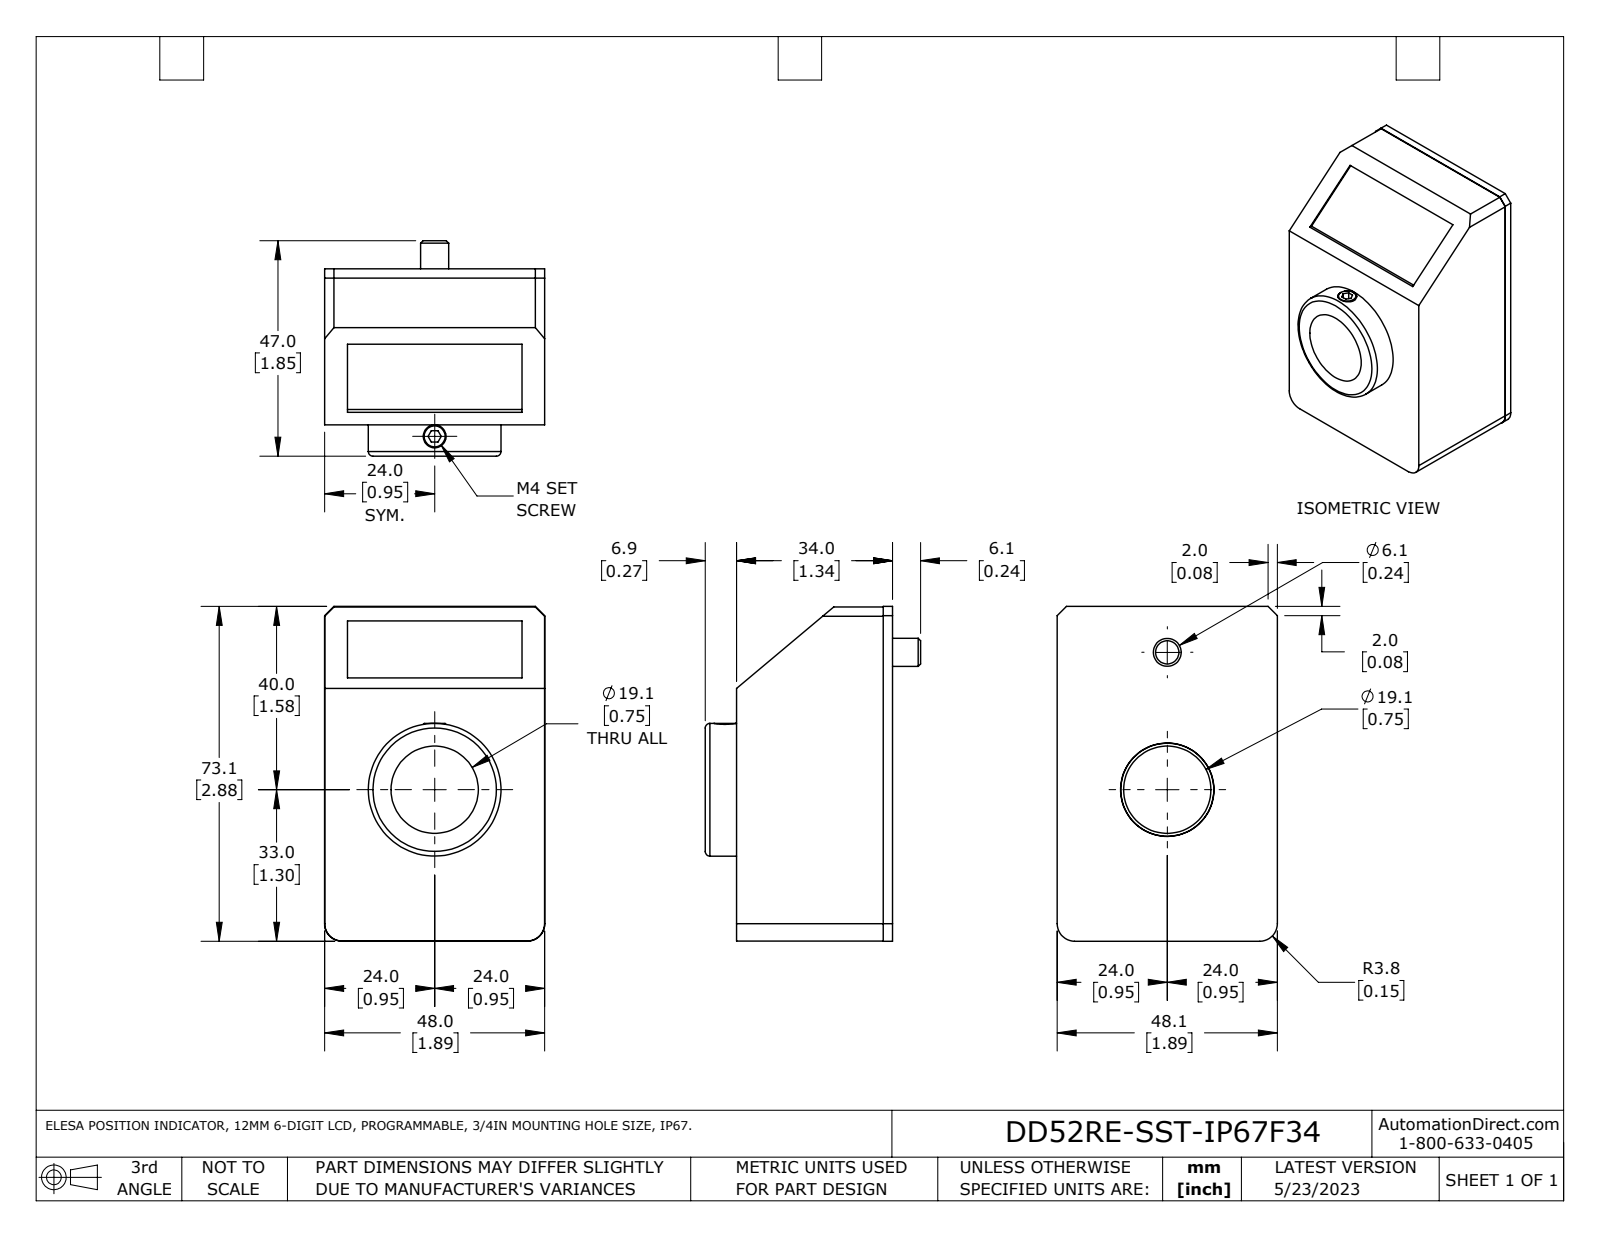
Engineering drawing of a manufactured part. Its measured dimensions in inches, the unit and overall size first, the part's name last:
Units: inches
Overall size (bounding box): 2.876 × 1.892 × 1.85
Round holes (diameter × count): ⌀0.196 ×1, ⌀0.75 ×1, ⌀0.802 ×1, ⌀1.14 ×1
Round bosses / shafts (diameter × count): ⌀0.8 ×1, ⌀0.24 ×1
Partial cylindrical surfaces — rounded edges, fillets, slot ends (radius × count): R0.15 ×4
Main face-to-face distances: 1.89, 1.34, 0.015, 2.87, 0.2, 1.14, 0.18, 0.02, 1.16, 1.891
Volume: 6.176 in³ · Surface area: 27.4 in²
Bodies: 1 solid, 51 faces (35 planar, 13 cylindrical, 3 other)
Part name (STEP PRODUCT): DD52RE-SST-IP67F34
STEP written by: SolidWorks 2021 (AUTOMOTIVE_DESIGN)
